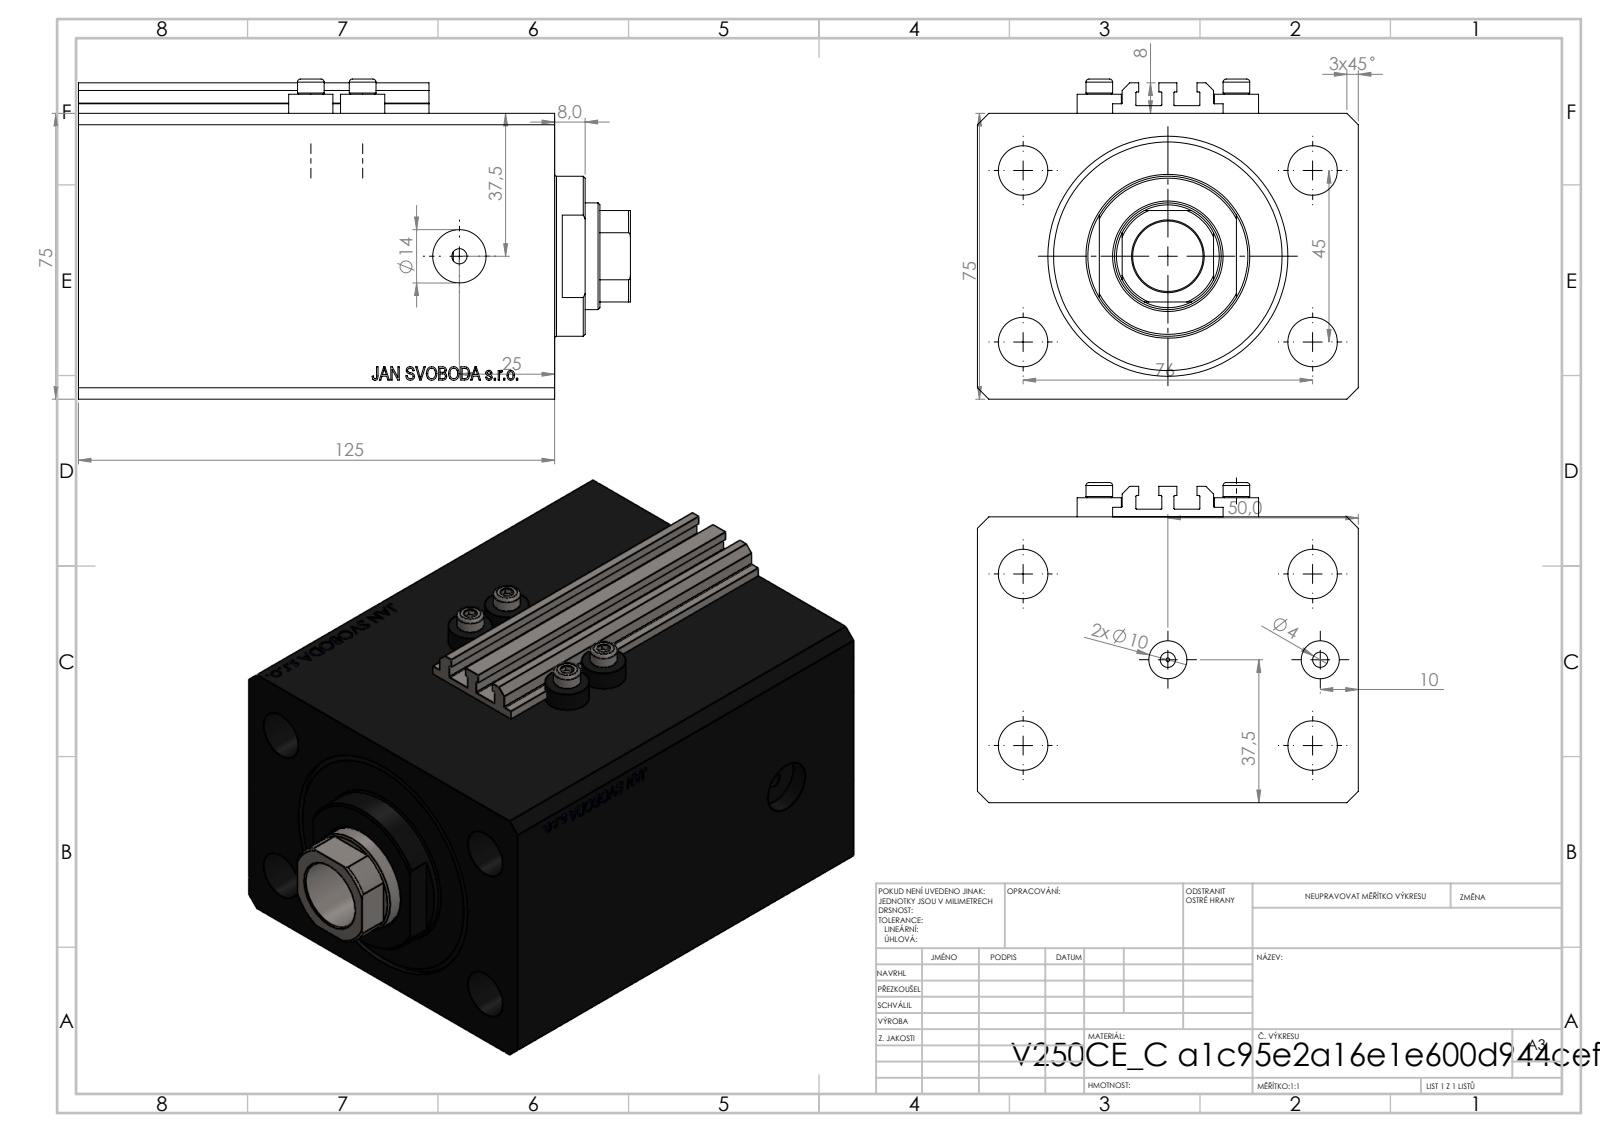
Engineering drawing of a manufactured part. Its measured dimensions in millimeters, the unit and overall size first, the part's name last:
Units: millimetres
Overall size (bounding box): 144.9 × 100 × 84
Round holes (diameter × count): ⌀4 ×8, ⌀13 ×4, ⌀10 ×2, ⌀14 ×2, ⌀1.25 ×1, ⌀18.5 ×1, ⌀28 ×1, ⌀50 ×1, ⌀63 ×1
Round bosses / shafts (diameter × count): ⌀11.6 ×4, ⌀7 ×4, ⌀42 ×1
Partial cylindrical surfaces — rounded edges, fillets, slot ends (radius × count): R0.2 ×10, R13.5 ×1
Main face-to-face distances: 75, 100, 125, 11.9, 113.1, 98.4, 86.5, 26.6, 48.4, 8
Hole centre spacings: 44.16, 13.6, 22.59, 36, 38.48, 45, 76, 81.18
Volume: 819 539 mm³ · Surface area: 144 653 mm²
Bodies: 8 solids, 1038 faces (504 planar, 88 cylindrical, 446 other)
Part name (STEP PRODUCT): V250CE_VC_C; V250CE_C_VCP; ALLEN BOLT V250CE; V250CE_C_Body
STEP written by: SolidWorks 2019 (CONFIG_CONTROL_DESIGN)
